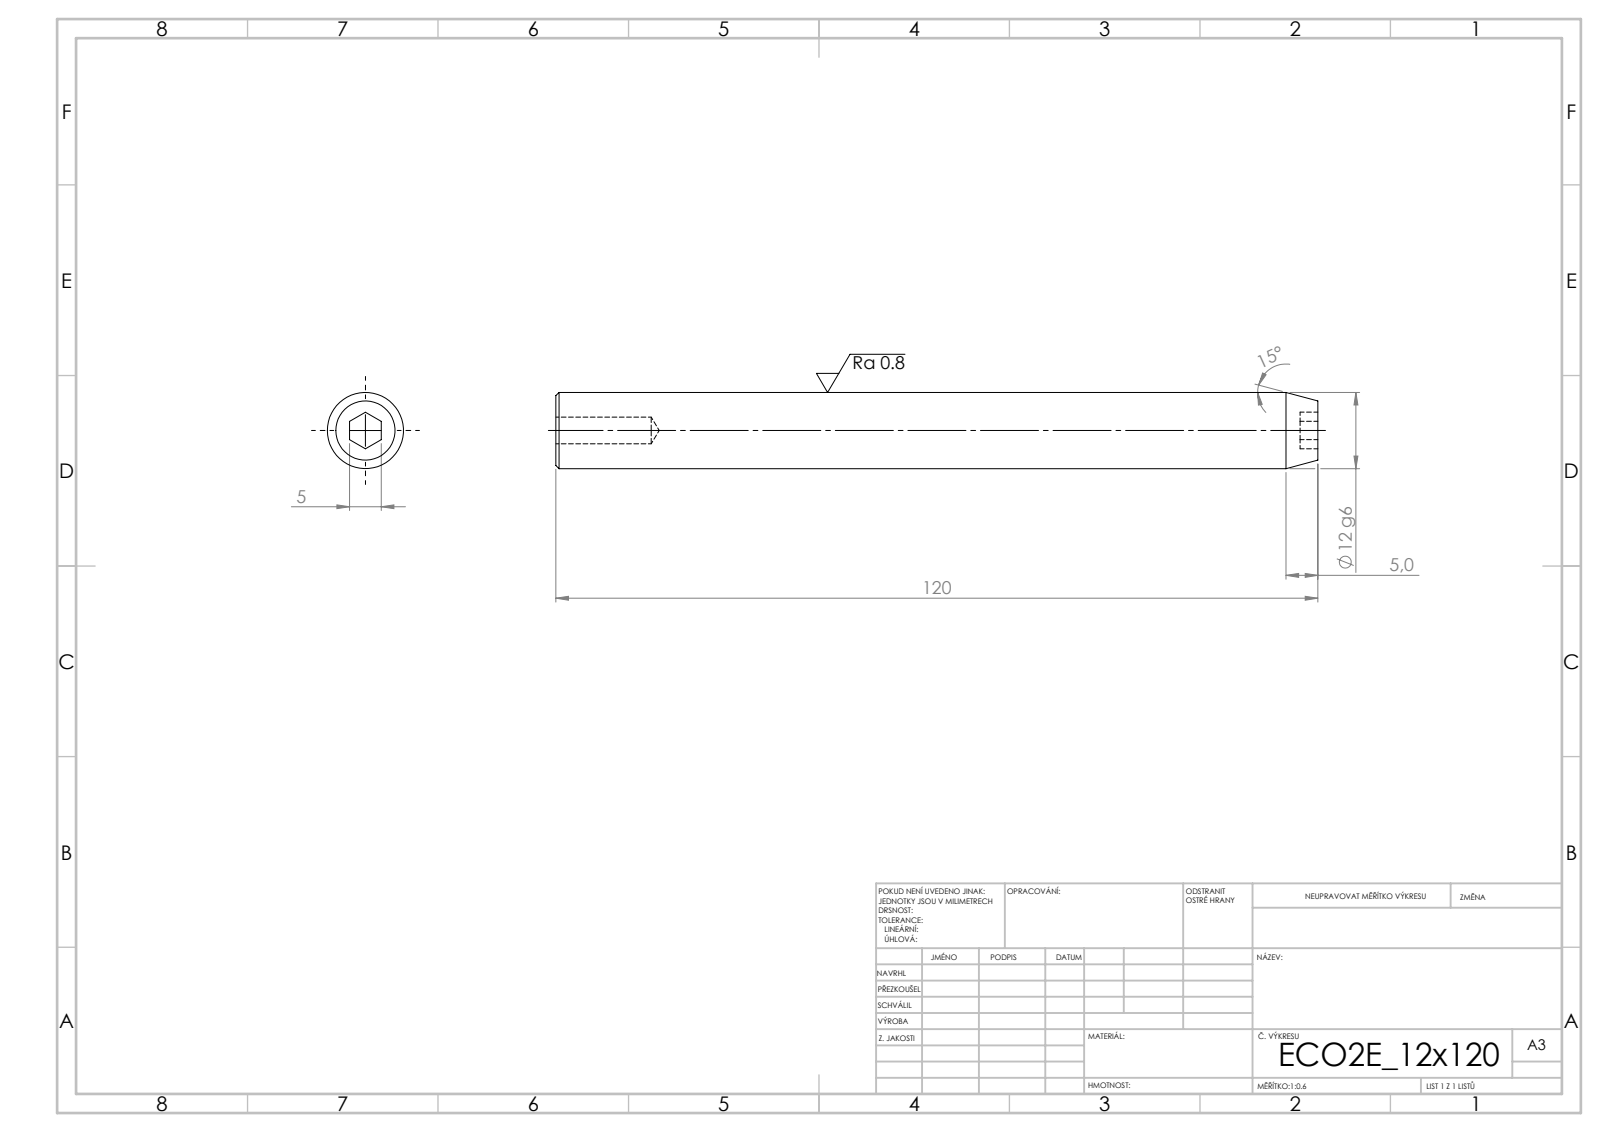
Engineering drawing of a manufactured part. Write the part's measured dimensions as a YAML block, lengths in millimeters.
step_written_by: "SolidWorks 2019 (CONFIG_CONTROL_DESIGN)"
units: millimeters
bodies: {solids: 1, faces: 19, planar: 9, cylindrical: 4, other: 6}
overall_size: [120, 12, 12]
volume: 13176
surface_area: 4927
round_holes:
  - {diameter: 4.2, count: 1}
round_bosses_or_shafts:
  - {diameter: 12, count: 1}
face_to_face_distances: [120, 5, 2.8, 117.2]
